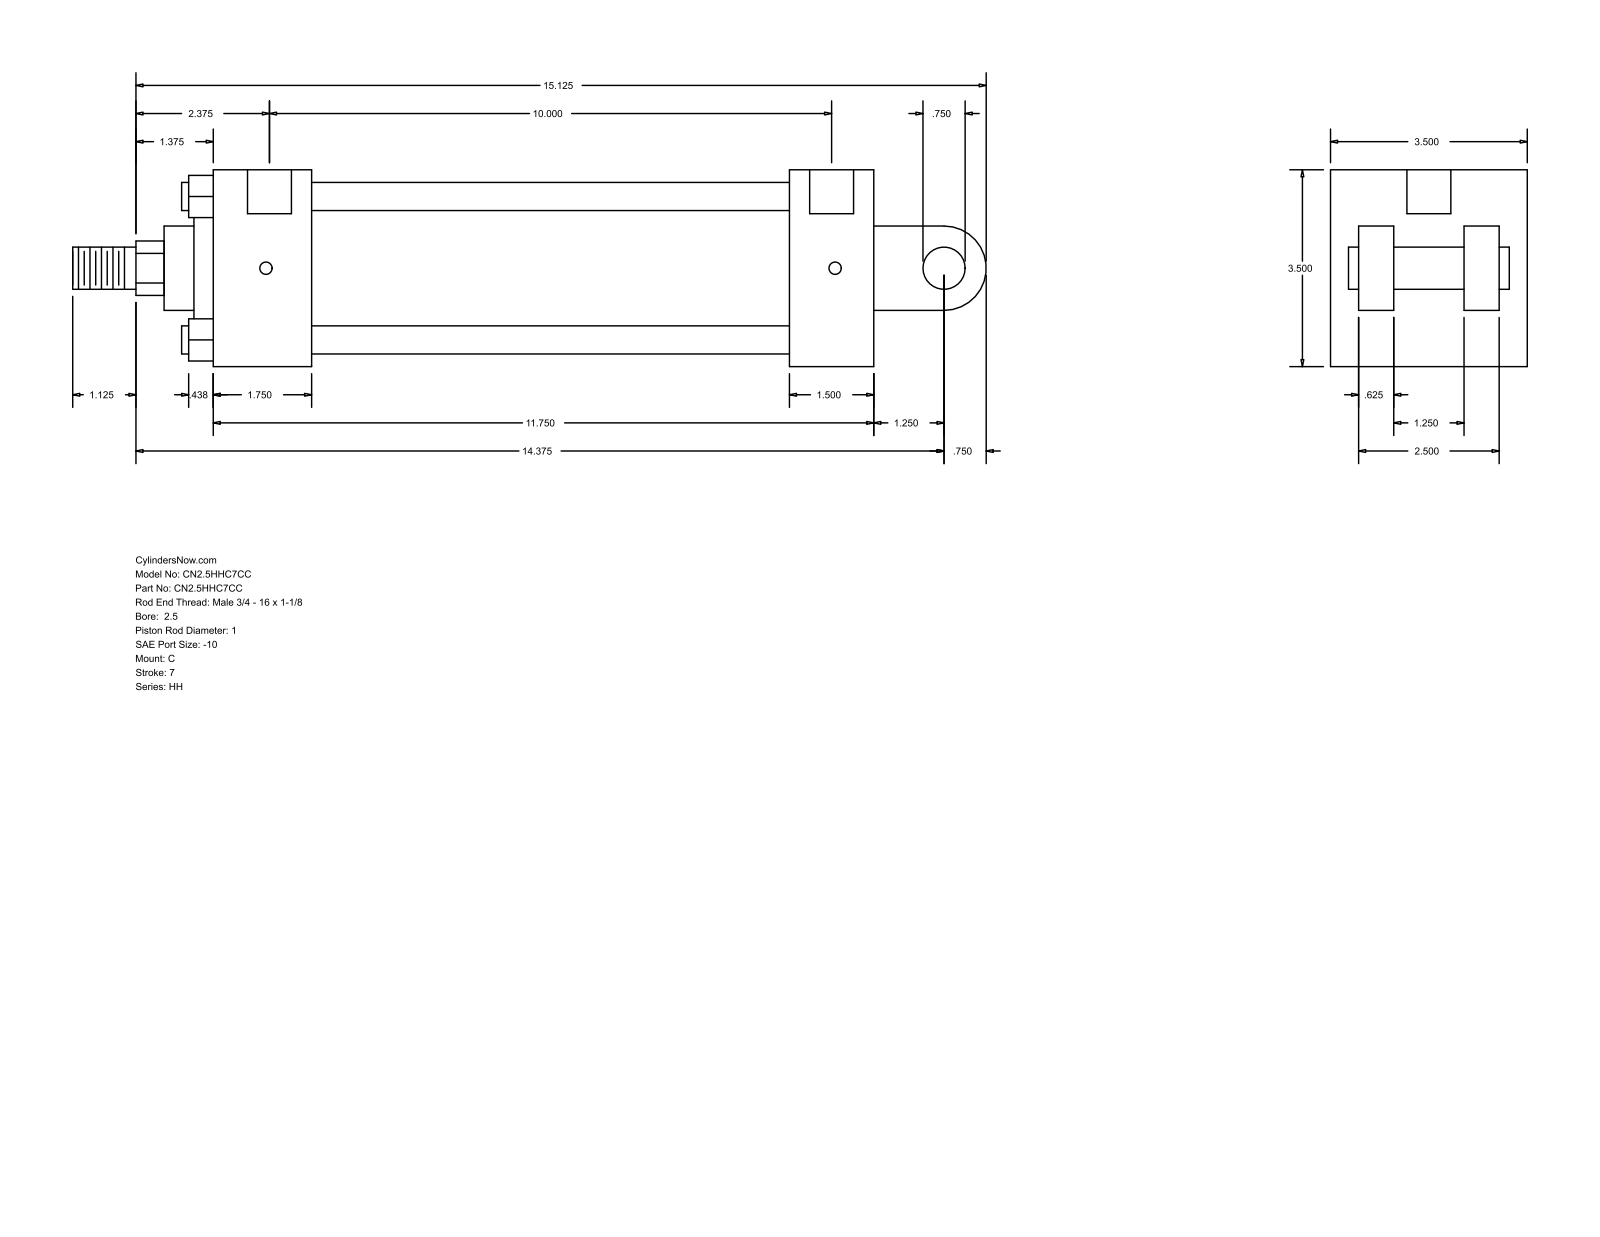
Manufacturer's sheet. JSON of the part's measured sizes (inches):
{"part_name": "HH_C__0250_1", "step_written_by": "GSSL Pune (CONFIG_CONTROL_DESIGN)", "units": "inches", "bodies": {"solids": 0, "faces": 101, "planar": 71, "cylindrical": 30, "other": 0}, "overall_size": [16.25, 3.5, 3.5], "round_holes": [[0.219, 4], [0.781, 2]], "round_bosses_or_shafts": [[0.5, 4], [0.75, 2], [2.875, 1], [2.375, 1], [1.5, 1], [1, 1]], "partial_cylinders_radius": [[0.484, 1], [0.75, 1]], "face_to_face_distances": [3.5, 11.75, 2.5, 10.25, 1.5, 1.75, 8.5, 10, 0.5, 1.125], "hole_center_spacings": [0.063, 10.062, 10.125, 10]}
